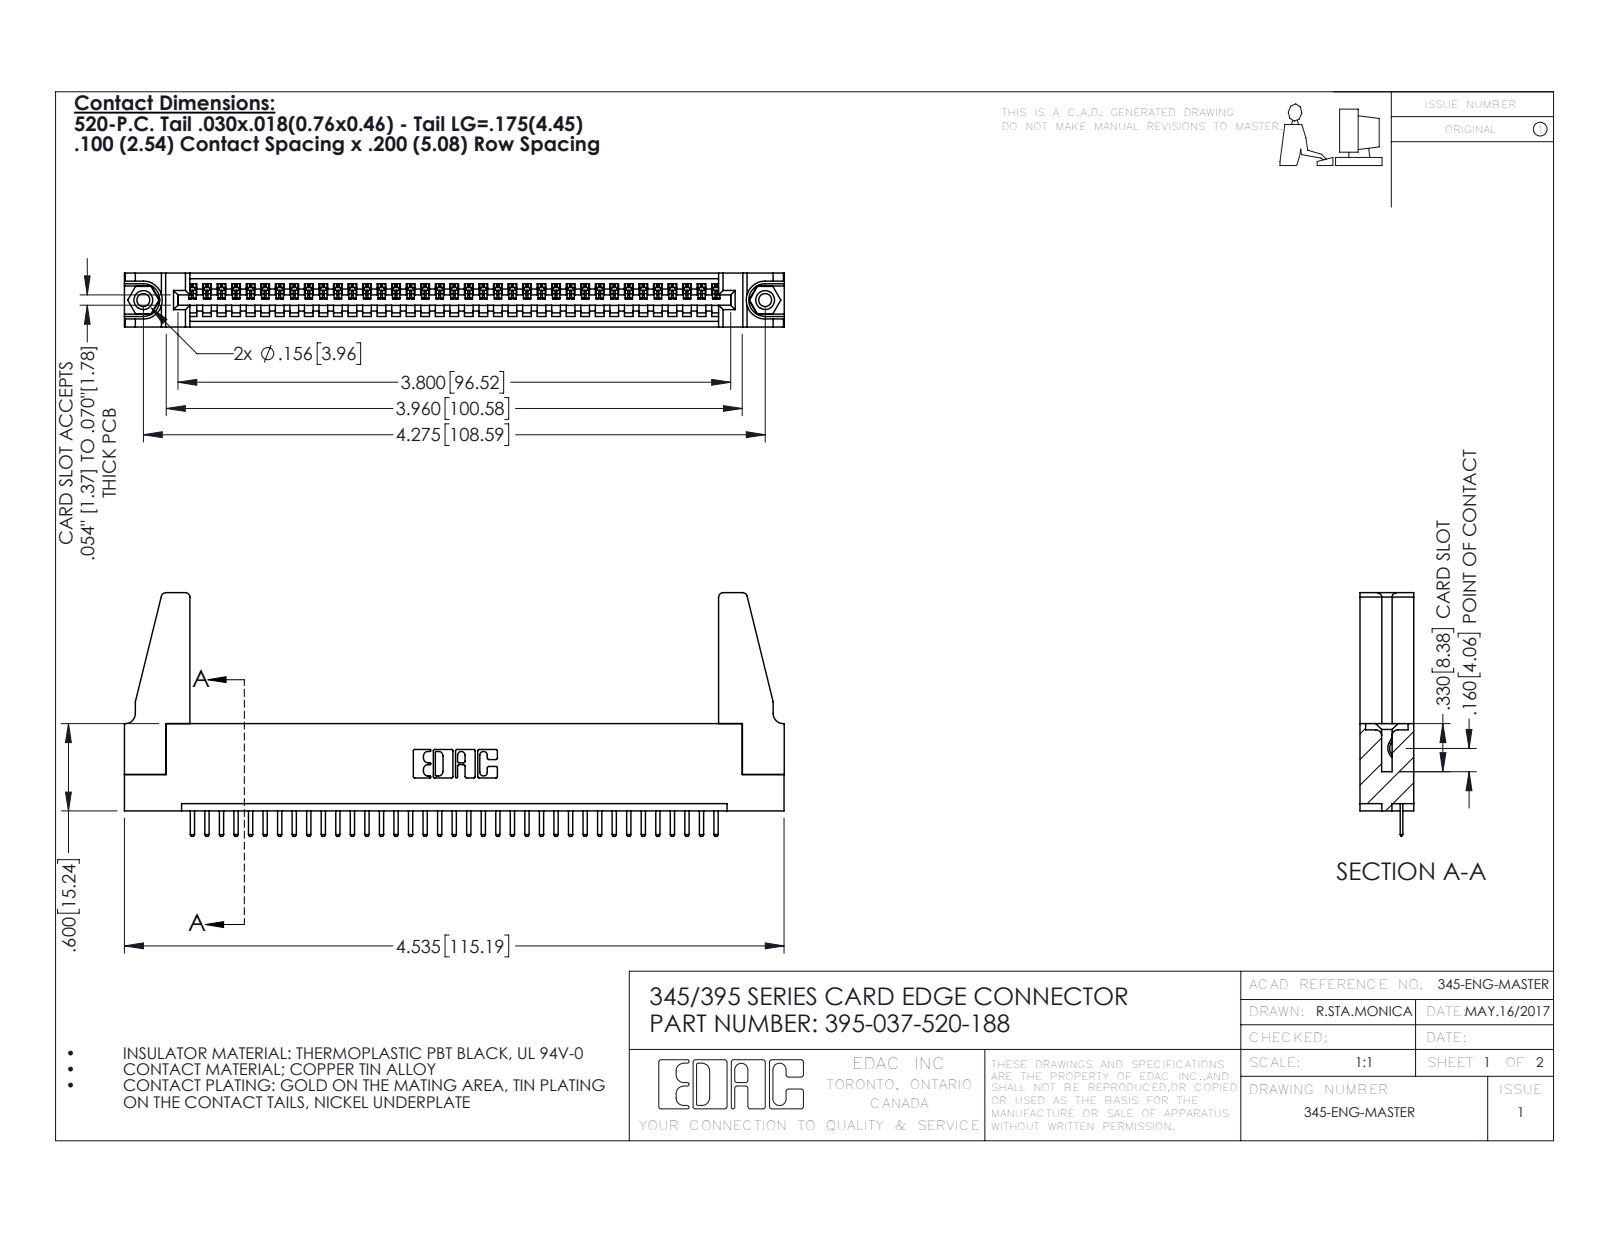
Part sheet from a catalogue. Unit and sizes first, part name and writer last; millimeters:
Units: millimetres
Overall size (bounding box): 115.2 × 42.5 × 9.4
Round holes (diameter × count): ⌀2.3 ×2, ⌀3.2 ×2, ⌀4 ×2, ⌀1.6 ×1
Round bosses / shafts (diameter × count): ⌀3.9 ×2
Partial cylindrical surfaces — rounded edges, fillets, slot ends (radius × count): R0.3 ×76, R0.2 ×74, R0.3 ×22, R0.8 ×8, R0.2 ×6, R0.8 ×6, R0.7 ×3, R0.8 ×2
Main face-to-face distances: 1.8, 9.4, 7.6, 5.1, 2.5, 6.9, 0.6, 5.7, 1.8, 3.8
Hole centre spacings: 6.9, 102.6, 108.6
Volume: 14 000 mm³ · Surface area: 17 060 mm²
Bodies: 42 solids, 2544 faces (1706 planar, 822 cylindrical, 16 other)
Part name (STEP PRODUCT): 345-250-001_345-250-001-102; 345 Part_Flush Mounting Lugs - 0.156 Dia-TH; 395-037-520-188; 345-220-078_345-220-088 (+1 more)
STEP written by: SolidWorks 2016 (CONFIG_CONTROL_DESIGN)
